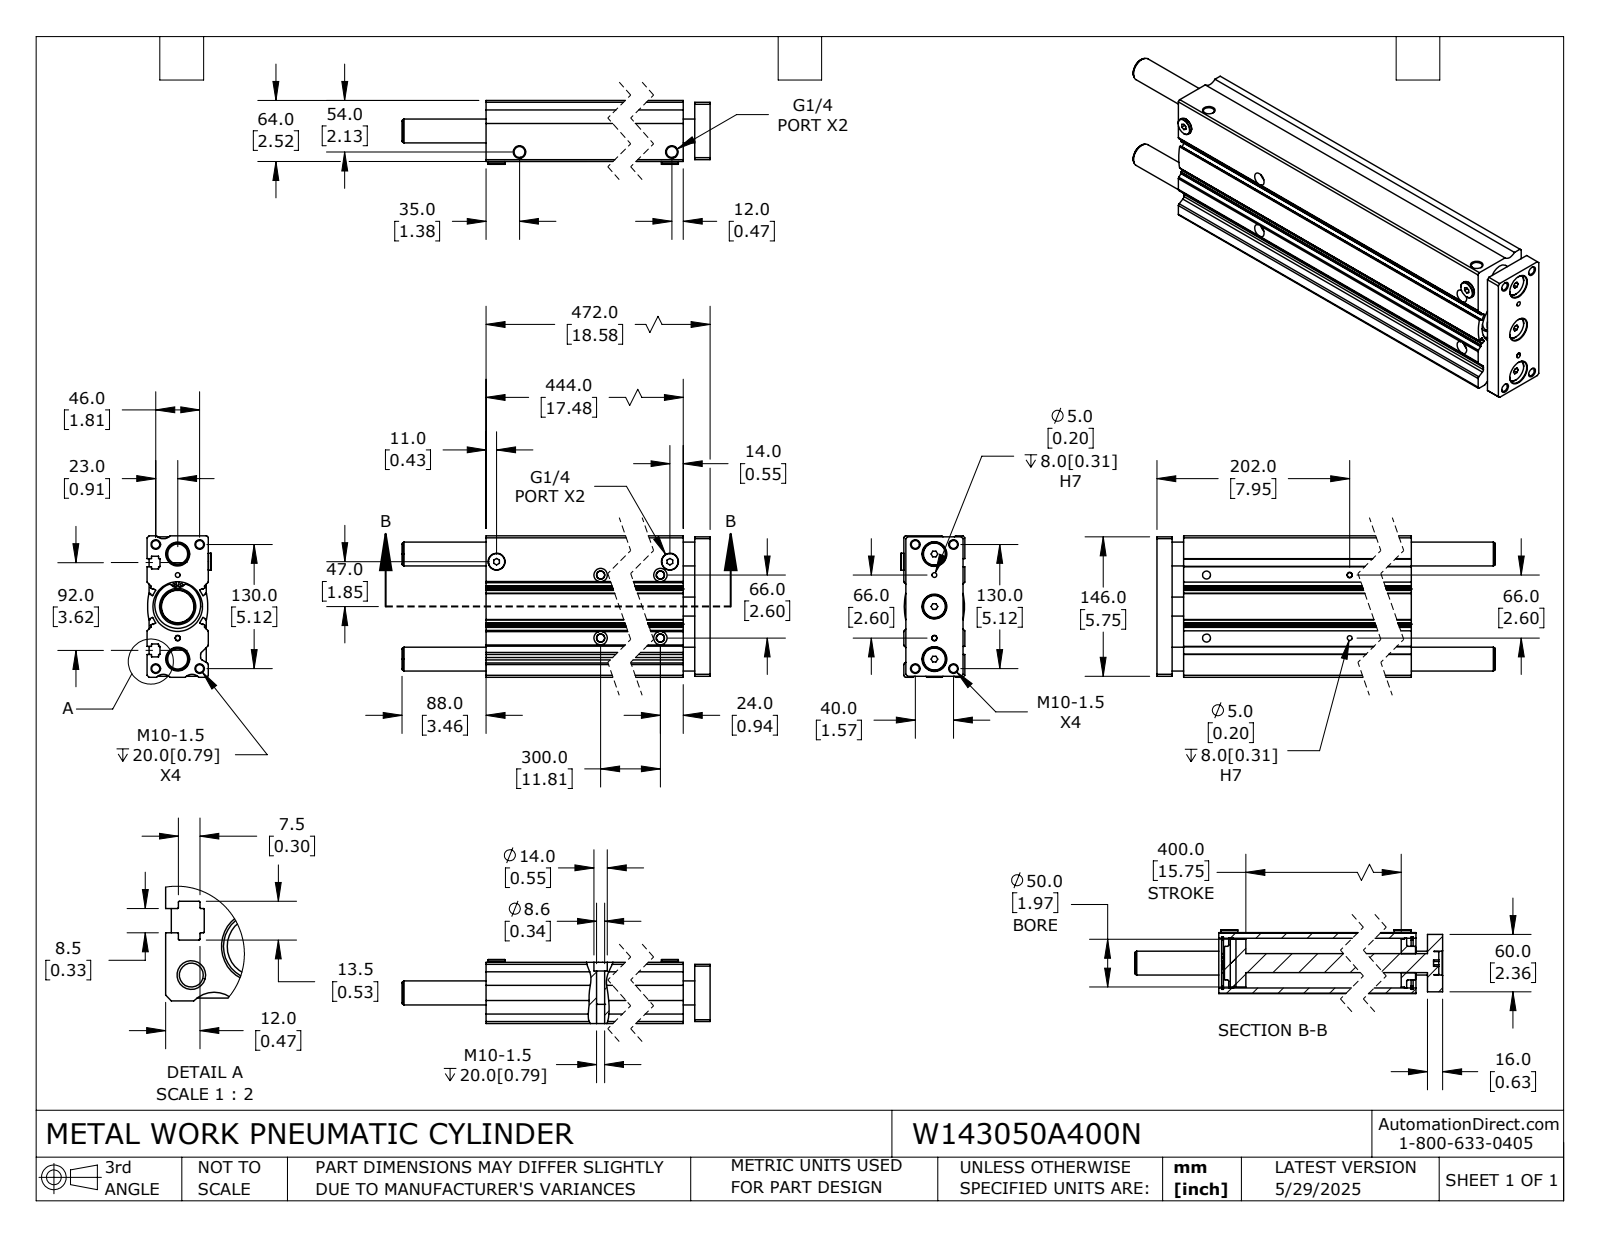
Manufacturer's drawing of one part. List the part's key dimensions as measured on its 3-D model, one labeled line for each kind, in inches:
Part name (STEP PRODUCT): W143050A400N; W143050A400N_BODY; W143050A400N_ROD
STEP written by: SolidWorks 2024 (CONFIG_CONTROL_DESIGN)
Units: inches
Bodies: 6 solids, 466 faces (186 planar, 224 cylindrical, 56 other)
Overall size (bounding box): 22.047 × 5.827 × 2.638
Volume: 202.1 in³ · Surface area: 892.8 in²
Round holes (diameter × count): ⌀0.33 ×12, ⌀0.098 ×4, ⌀0.197 ×4, ⌀0.339 ×4, ⌀0.551 ×4, ⌀0.984 ×3, ⌀0.451 ×2, ⌀1.89 ×2, ⌀0.787 ×1
Round bosses / shafts (diameter × count): ⌀0.945 ×3, ⌀0.697 ×2, ⌀2.165 ×1, ⌀2.047 ×1, ⌀1.969 ×1, ⌀1.378 ×1
Partial cylindrical surfaces — rounded edges, fillets, slot ends (radius × count): R0.012 ×44, R0.02 ×12, R0.118 ×10, R0.079 ×6, R2.677 ×6, R0.039 ×4, R0.098 ×4, R0.394 ×3
Main face-to-face distances: 2.52, 5.827, 0.472, 0.531, 0.098, 3.622, 0.433, 1.988, 17.48, 0.63
Hole centre spacings: 0.118, 0.424, 0.869, 0.88, 0.916, 0.963, 0.987, 1.271
